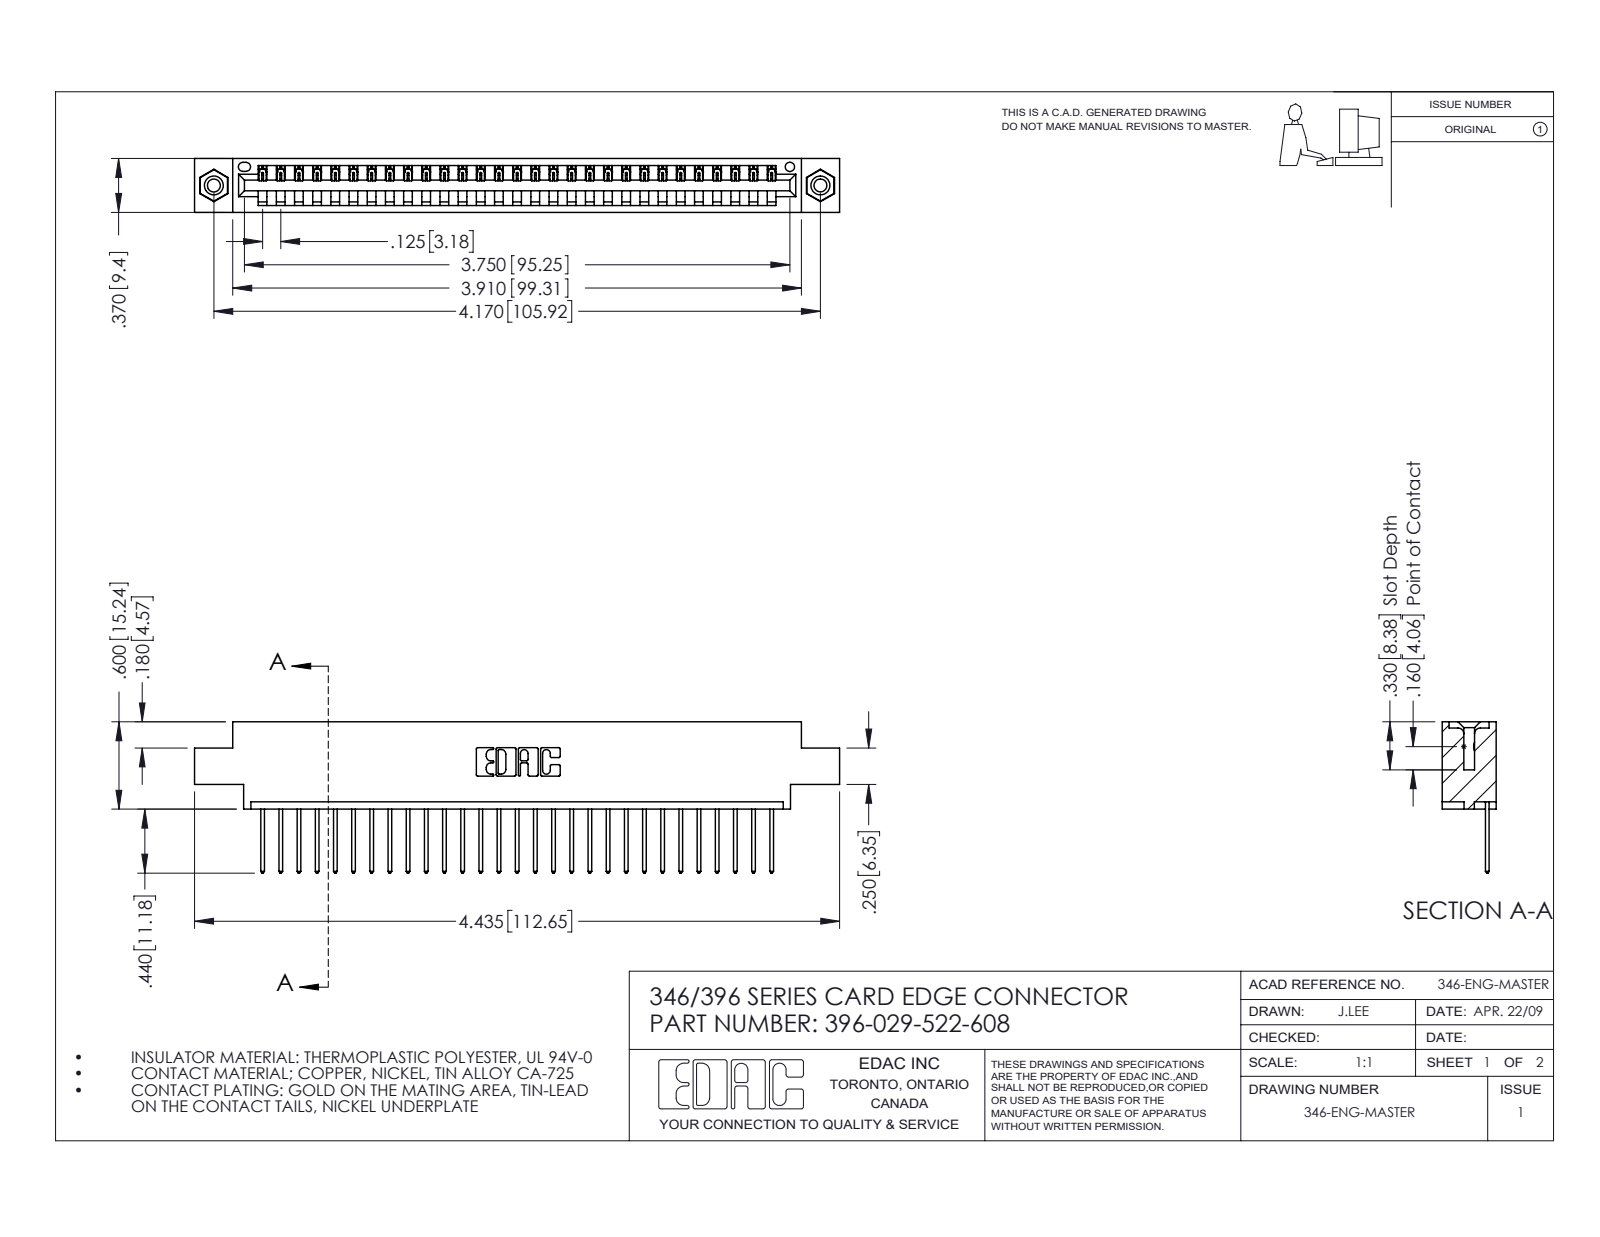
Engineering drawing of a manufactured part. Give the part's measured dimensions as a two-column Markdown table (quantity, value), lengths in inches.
| quantity | value |
| --- | --- |
| part name | 345-250-001_345-250-003-102; 345-292-001_345-293-122; 396-029-522-608; 346 Part_0.170 Offset - 0.156 Dia-TI |
| STEP written by | SolidWorks 2016 (CONFIG_CONTROL_DESIGN) |
| units | inches |
| bodies | 32 solids, 1868 faces (1272 planar, 580 cylindrical, 16 other) |
| overall size | 4.435 × 1.04 × 0.37 |
| volume | 0.643 in³ |
| surface area | 20.64 in² |
| round holes (diameter × count) | 0.089 × 2, 0.125 × 2, 0.156 × 2, 0.064 × 1 |
| round bosses / shafts (diameter × count) | 0.155 × 2 |
| partial cylindrical surfaces (radius × count) | 0.006 × 58, 0.01 × 58, 0.01 × 22, 0.007 × 6, 0.031 × 6, 0.026 × 3, 0.031 × 2, 0.04 × 2 |
| main face-to-face distances | 0.048, 0.322, 0.37, 0.25, 0.072, 0.298, 0.025, 0.222, 0.148, 0.1 |
| hole center spacings | 0.246, 3.962, 4.17 |
